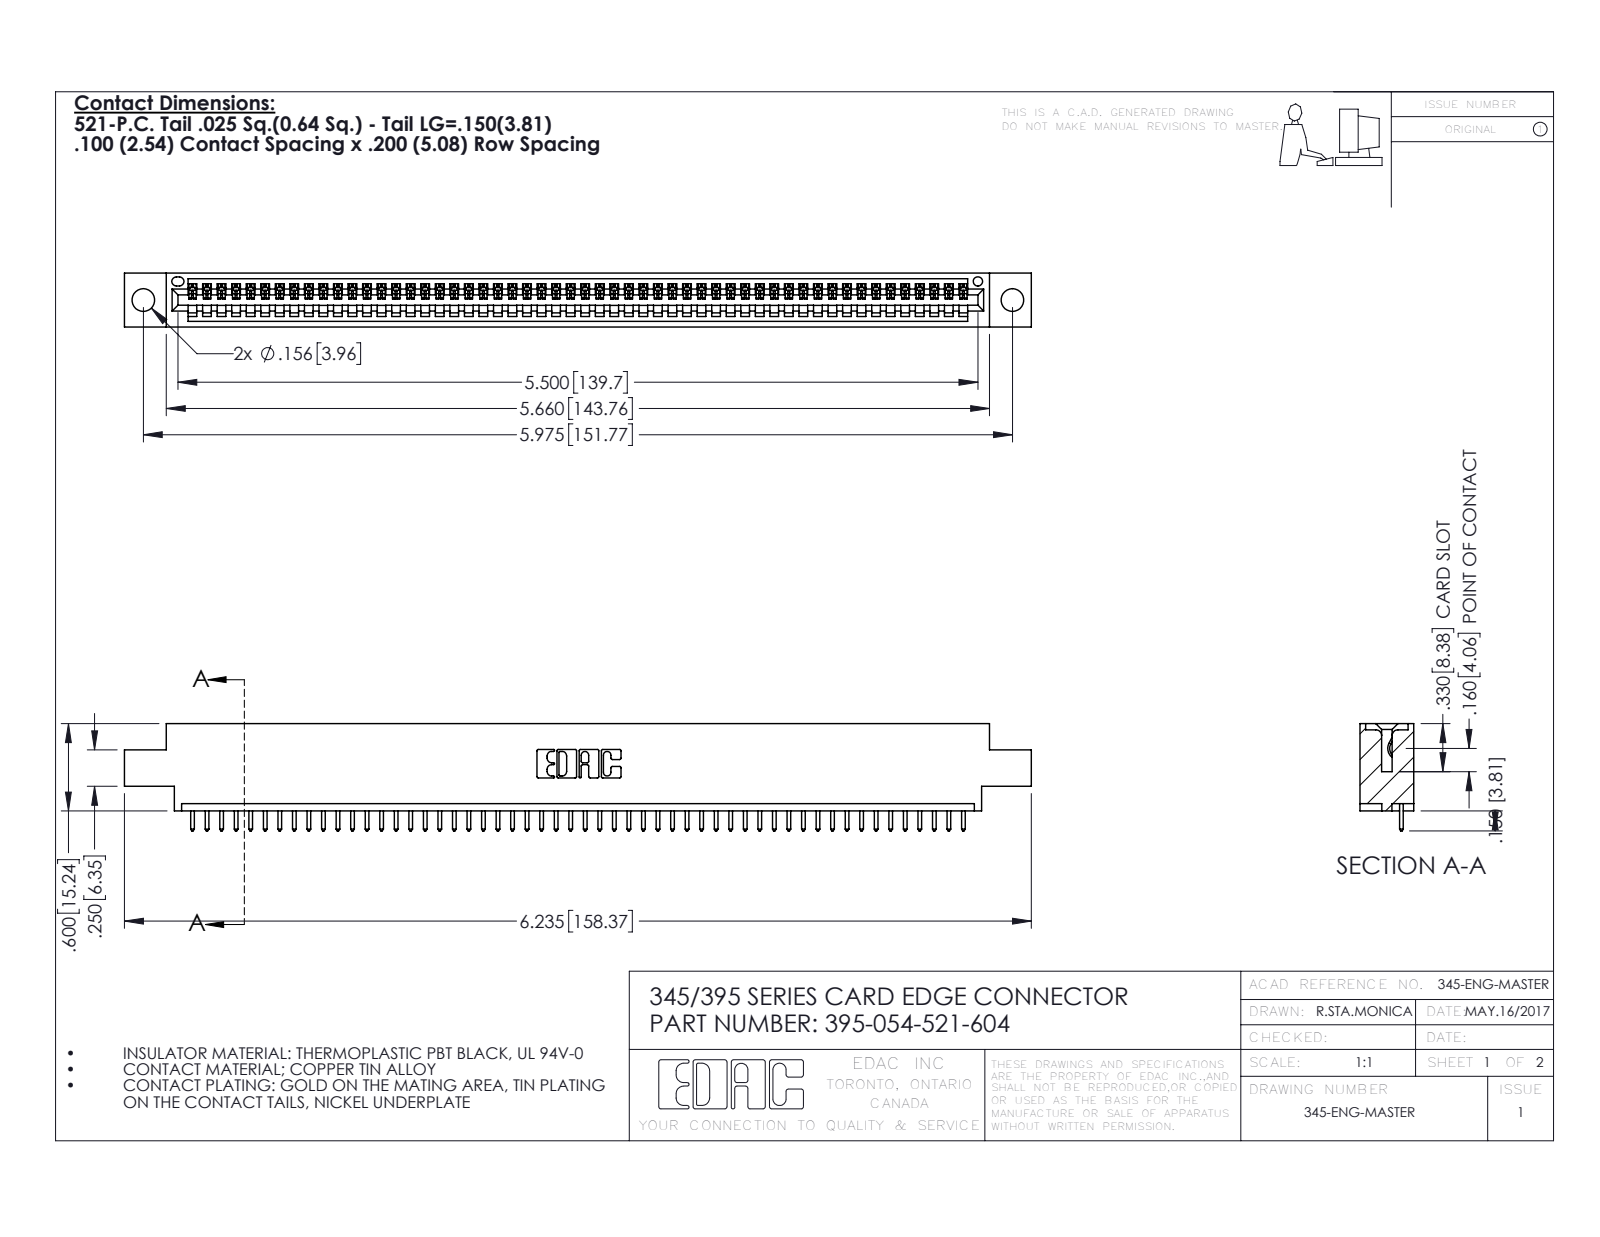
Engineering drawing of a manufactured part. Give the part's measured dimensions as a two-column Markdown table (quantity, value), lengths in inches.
| quantity | value |
| --- | --- |
| part name | 395-054-521-604; 345 Part_0.170 Offset - 0.156 Dia-TH; 345-292-001_345-293-121 |
| STEP written by | SolidWorks 2016 (CONFIG_CONTROL_DESIGN) |
| units | inches |
| bodies | 55 solids, 3262 faces (2244 planar, 1018 cylindrical, 0 other) |
| overall size | 6.235 × 0.737 × 0.37 |
| volume | 0.902 in³ |
| surface area | 29.68 in² |
| round holes (diameter × count) | 0.156 × 2, 0.064 × 1 |
| partial cylindrical surfaces (radius × count) | 0.006 × 108, 0.01 × 108, 0.01 × 22, 0.007 × 6, 0.031 × 6, 0.026 × 3, 0.031 × 2, 0.04 × 2 |
| main face-to-face distances | 0.298, 0.072, 0.37, 0.2, 0.098, 0.272, 0.025, 0.225, 0.175, 0.149 |
| hole center spacings | 0.27, 5.739, 5.975 |
